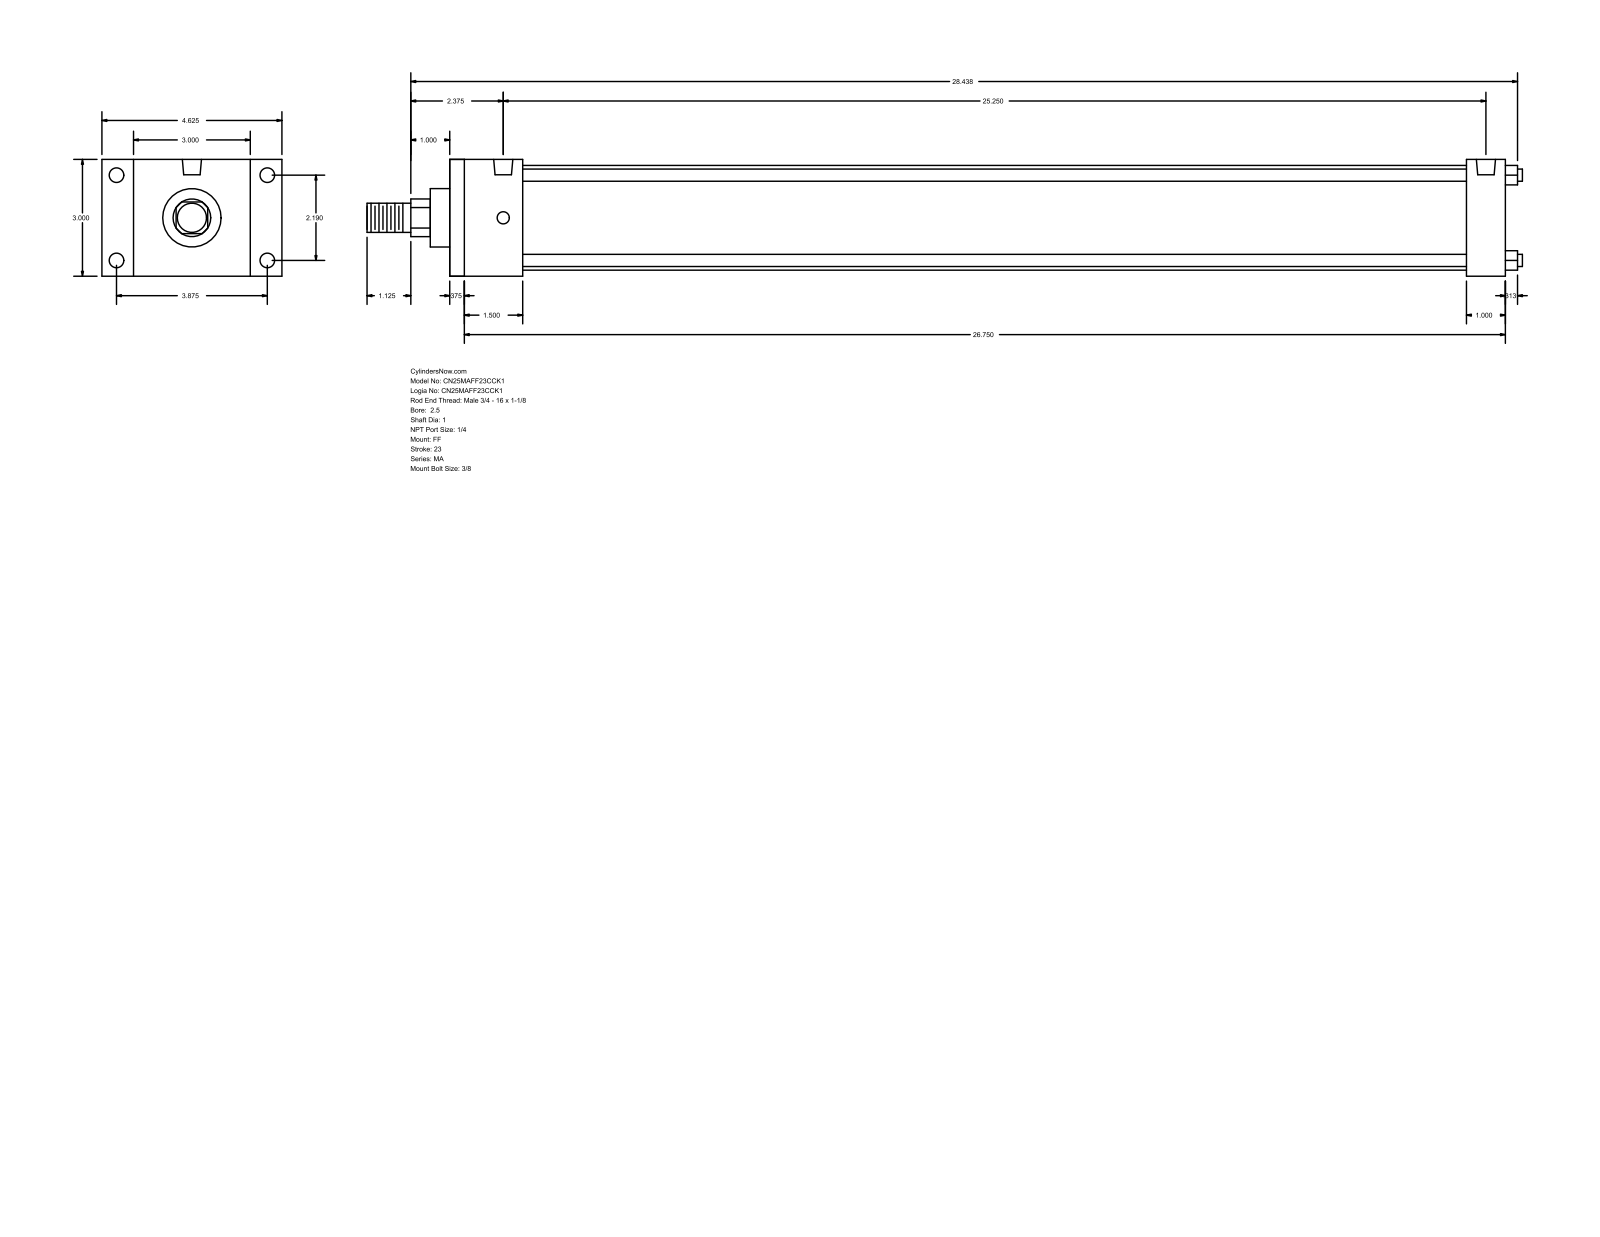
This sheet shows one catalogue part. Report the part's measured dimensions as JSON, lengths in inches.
{"part_name": "MA_FF__0250_1", "step_written_by": "GSSL Pune (CONFIG_CONTROL_DESIGN)", "units": "inches", "bodies": {"solids": 0, "faces": 92, "planar": 64, "cylindrical": 28, "other": 0}, "overall_size": [29.687, 4.625, 3], "round_holes": [[0.313, 4], [0.375, 4], [0.492, 2]], "round_bosses_or_shafts": [[0.313, 4], [2.69, 1], [1.5, 1], [1, 1], [0.75, 1]], "partial_cylinders_radius": [[0.484, 1]], "face_to_face_distances": [3, 27.125, 0.375, 26.75, 1, 1.875, 26.125, 1.5, 25.75, 24.25], "hole_center_spacings": [2.19, 3.875, 4.451, 25.25]}
